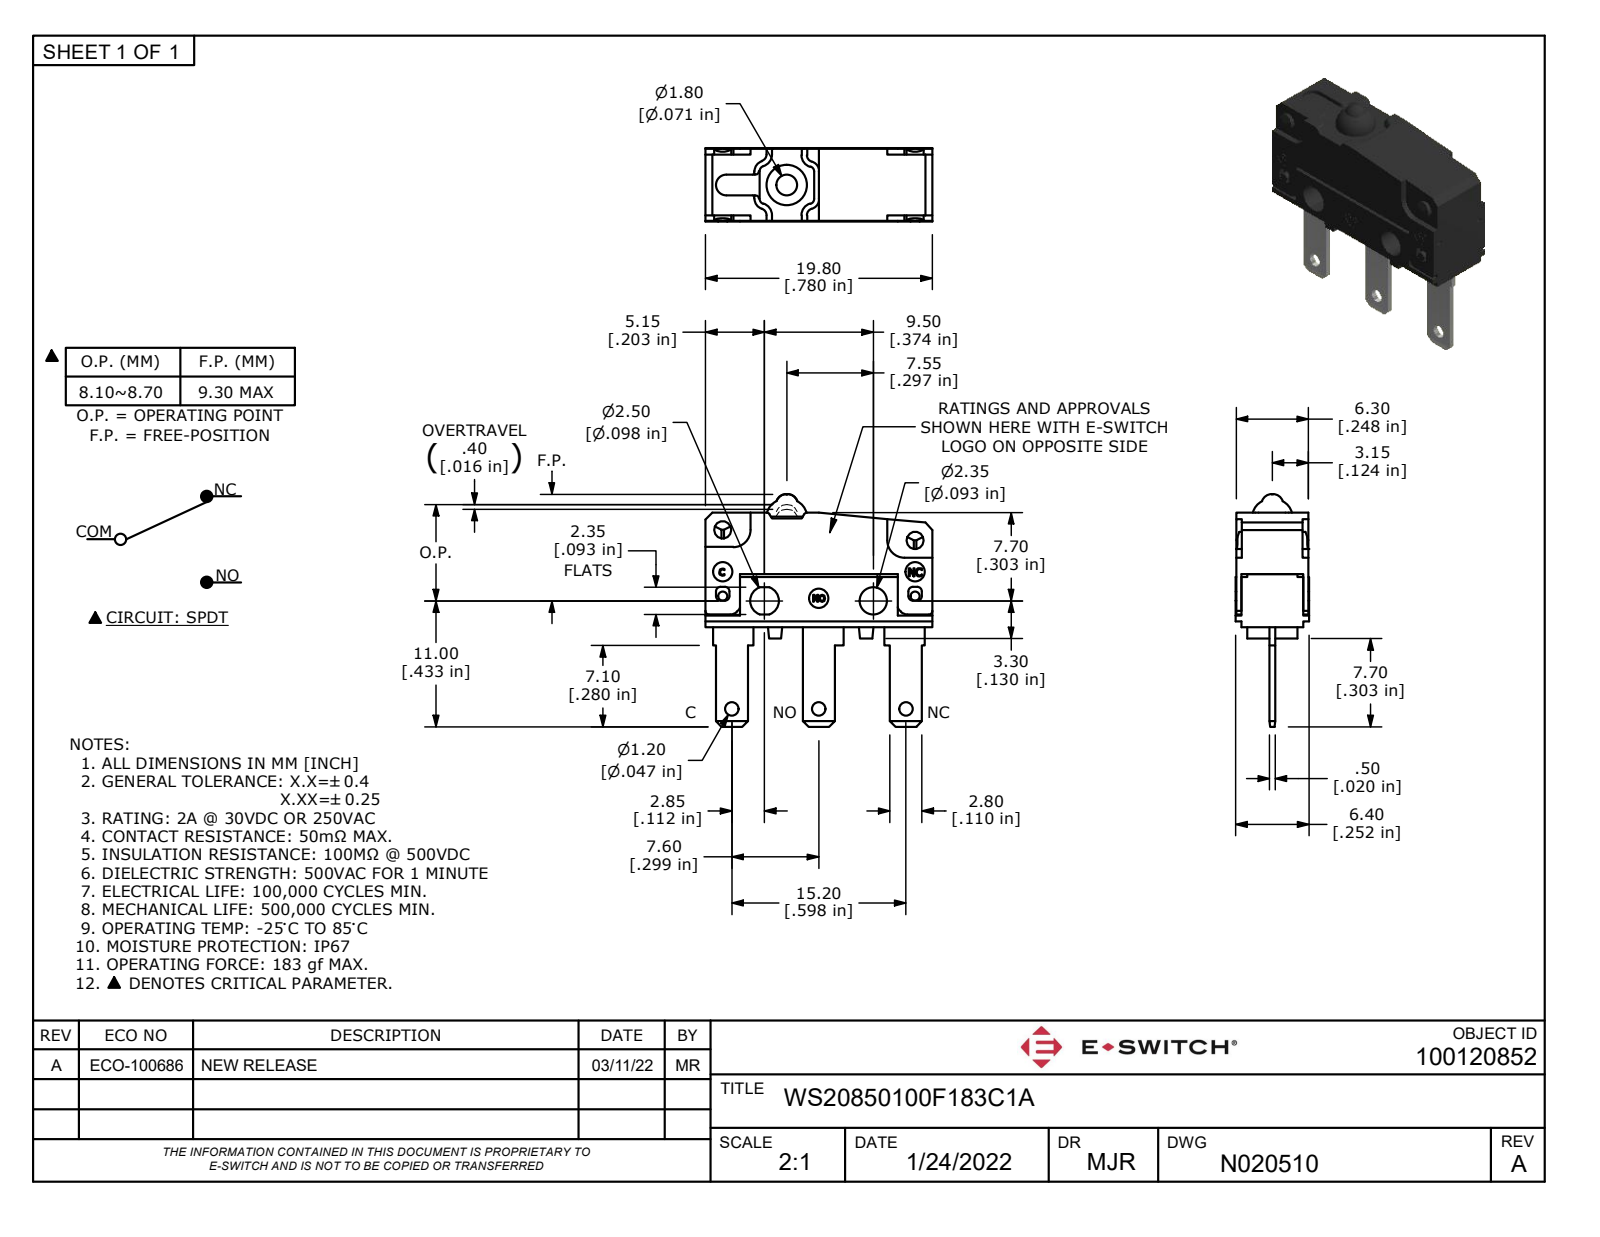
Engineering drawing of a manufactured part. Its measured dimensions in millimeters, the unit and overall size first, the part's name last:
Units: millimetres
Overall size (bounding box): 20.3 × 19.8 × 6.4
Round holes (diameter × count): ⌀1.2 ×3, ⌀1.7 ×3, ⌀2.35 ×1
Round bosses / shafts (diameter × count): ⌀1.5 ×2, ⌀0.8 ×2, ⌀3.5 ×1
Partial cylindrical surfaces — rounded edges, fillets, slot ends (radius × count): R0.3 ×10, R0.4 ×8, R0.1 ×2, R0.8 ×2, R1.5 ×2, R0.9 ×1, R1.25 ×1
Main face-to-face distances: 0.5, 2.9, 3.4, 2.95, 3.45, 6.35, 6.3, 5.85, 19.8, 0.45
Hole centre spacings: 7.6, 8.71, 11.97, 12.28, 14.6, 19.96, 4.44, 4.76
Volume: 1 166 mm³ · Surface area: 1 151 mm²
Bodies: 1 solid, 374 faces (235 planar, 68 cylindrical, 71 other)
Part name (STEP PRODUCT): WS20850100F183C1A
STEP written by: Autodesk Inventor 2020 (AUTOMOTIVE_DESIGN)
